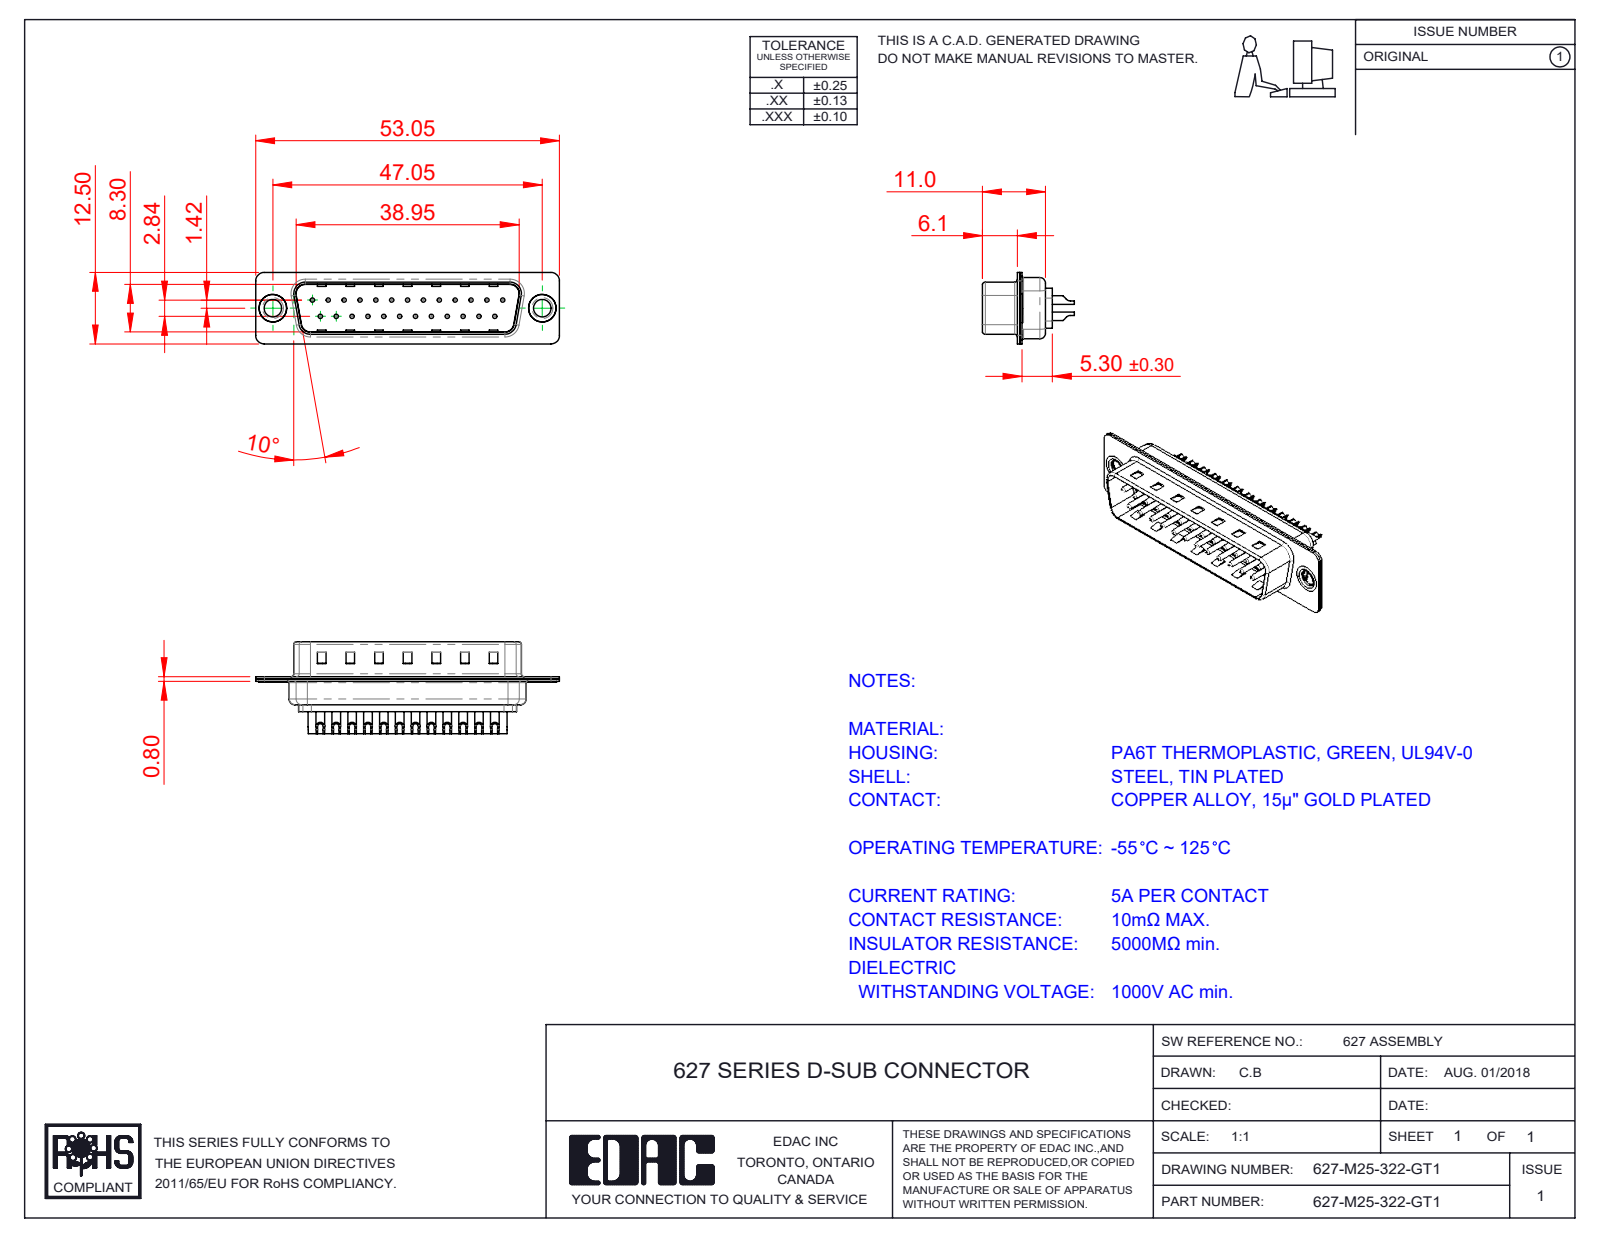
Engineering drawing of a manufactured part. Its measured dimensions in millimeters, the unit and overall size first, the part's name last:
Units: millimetres
Overall size (bounding box): 53.05 × 16.05 × 12.5
Round holes (diameter × count): ⌀0.75 ×25, ⌀1 ×25, ⌀1.6 ×25, ⌀2 ×25, ⌀3.05 ×2, ⌀4 ×2, ⌀4.8 ×2
Round bosses / shafts (diameter × count): ⌀1.5 ×25, ⌀5 ×2, ⌀4.9 ×2, ⌀3.55 ×2
Partial cylindrical surfaces — rounded edges, fillets, slot ends (radius × count): R1.5 ×16, R2 ×12, R0.5 ×8, R1.6 ×8, R1 ×6, R0.25 ×4, R0.6 ×4, R0.65 ×4
Main face-to-face distances: 0.4, 0.8, 9.5, 9.1, 8.7, 9.9, 1.2, 0.75, 0.35, 6.1
Hole centre spacings: 3.16, 2.77, 5.54, 8.31, 11.08, 13.85, 16.62, 5.03
Volume: 2 698 mm³ · Surface area: 6 932 mm²
Bodies: 30 solids, 1275 faces (396 planar, 521 cylindrical, 358 other)
Part name (STEP PRODUCT): 627M Contact Row 1_22; 627M Housing_25 Contacts; 627M Shell Front_25 Contacts; 627M Thru Hole Rivet (+3 more)
STEP written by: SolidWorks 2020 (CONFIG_CONTROL_DESIGN)
